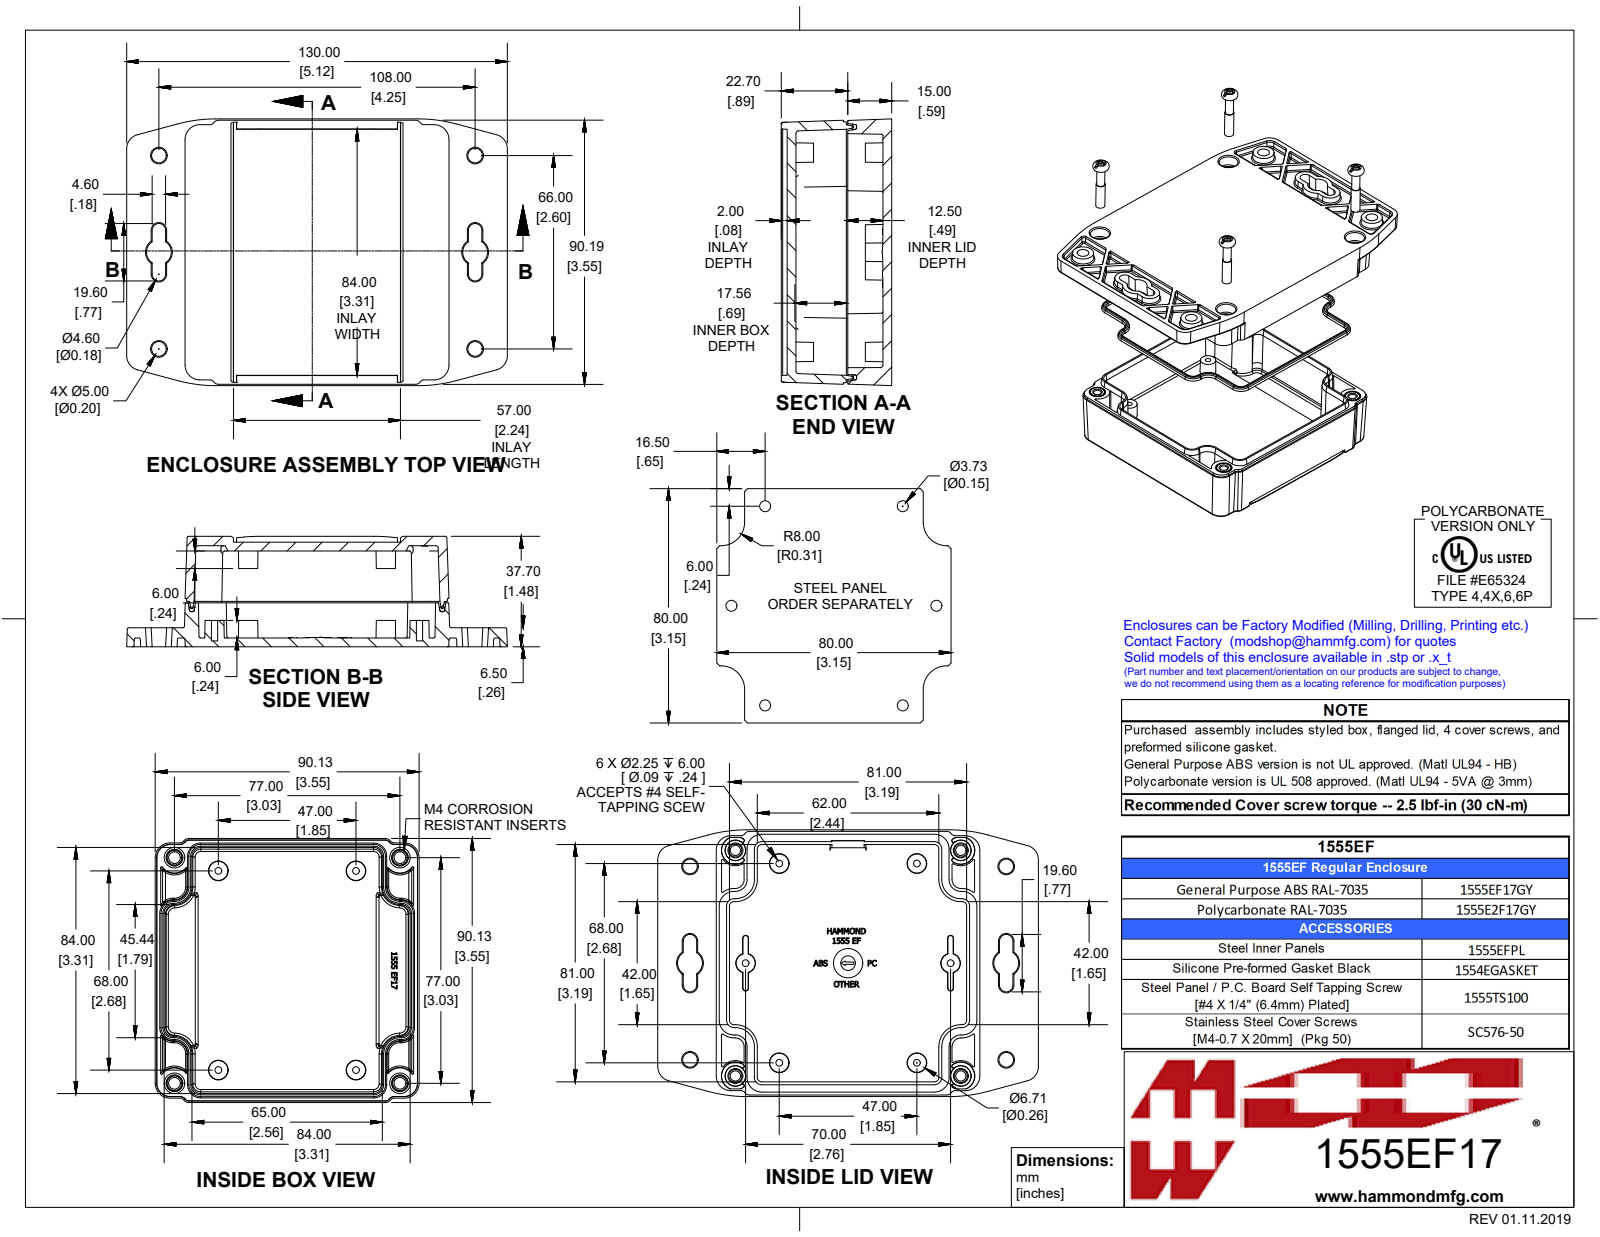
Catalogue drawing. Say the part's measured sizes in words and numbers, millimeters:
The part is named "1555EF17GY". Its 3-D file was written by "SolidWorks 2019 (CONFIG_CONTROL_DESIGN)". It is 11 solids with 2395 faces: 779 planar, 490 cylindrical and 1126 other. Overall it measures 130 by 91.1 by 37.7 millimeters. Its volume is 112 800 cubic millimeters and its surface area 80 390 square millimeters. Round holes: 6 of diameter 2.3, 4 of diameter 3.3, 4 of diameter 7. Round bosses or shafts: 4 of diameter 6.4, 4 of diameter 5.5, 4 of diameter 5.3, 4 of diameter 3.9, 4 of diameter 3.4, 1 of diameter 10, 1 of diameter 5. Partial cylindrical surfaces (rounded edges, fillets, slot ends): 165 of radius 0.5, 13 of radius 0.8, 6 of radius 0.3, 4 of radius 3, 4 of radius 5, 4 of radius 5.1, 4 of radius 50, 2 of radius 1. The main face-to-face distances are 3, 32.7, 29.7, 35.7, 2, 6.5, 3.5, 3.1, 3, 26.2. The hole center spacings are 15.7, 35.9, 38.7, 62.2, 67.7, 74, 77, 83.
